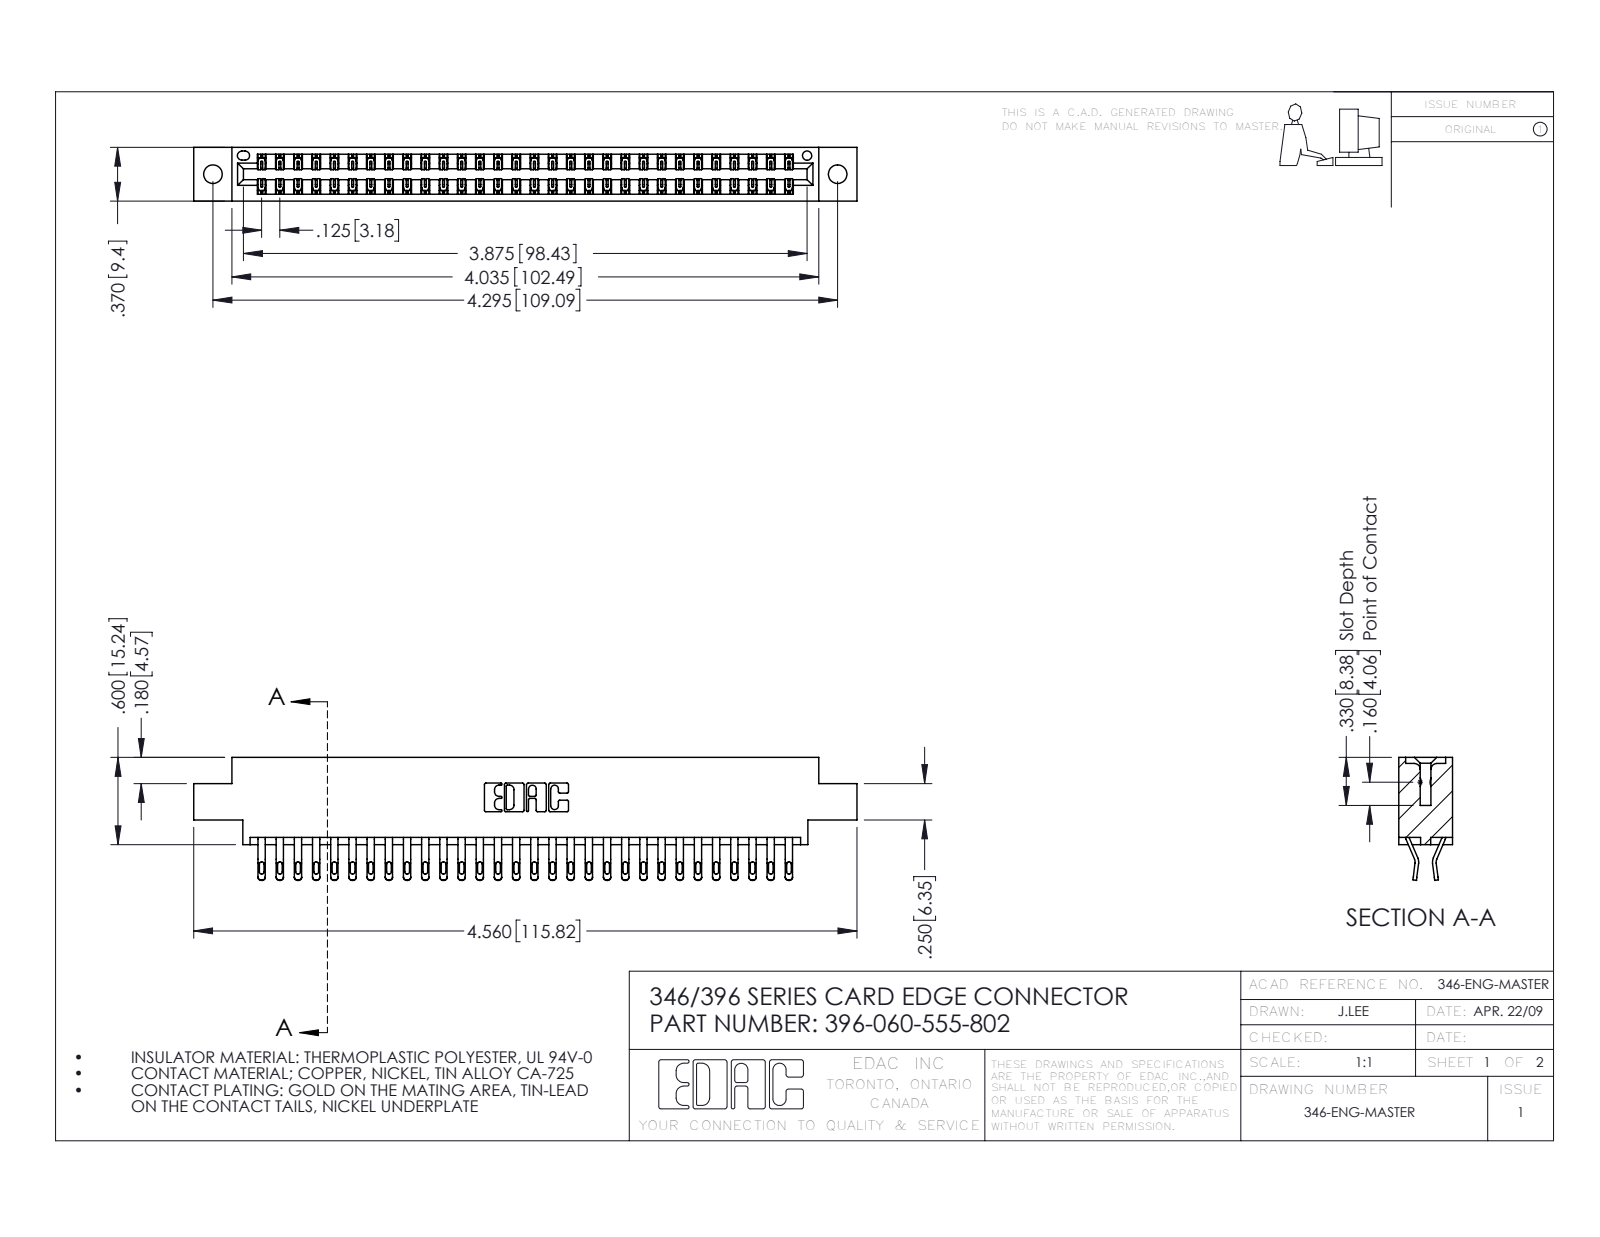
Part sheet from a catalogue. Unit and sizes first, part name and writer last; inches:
Units: inches
Overall size (bounding box): 4.56 × 0.845 × 0.37
Round holes (diameter × count): ⌀0.128 ×2, ⌀0.064 ×1
Partial cylindrical surfaces — rounded edges, fillets, slot ends (radius × count): R0.016 ×120, R0.02 ×120, R0.006 ×90, R0.01 ×22, R0.007 ×6, R0.031 ×6, R0.026 ×3, R0.01 ×2
Main face-to-face distances: 0.048, 0.322, 0.37, 0.25, 0.025, 0.072, 0.298, 0.275, 0.148, 0.222
Hole centre spacings: 0.246, 4.087, 4.295
Volume: 0.682 in³ · Surface area: 24.36 in²
Bodies: 61 solids, 3606 faces (2060 planar, 1546 cylindrical, 0 other)
Part name (STEP PRODUCT): 346 Part_0.170 Offset - 0.128 Dia; 396-060-555-802; 345-292-001_555 Tail
STEP written by: SolidWorks 2016 (CONFIG_CONTROL_DESIGN)
